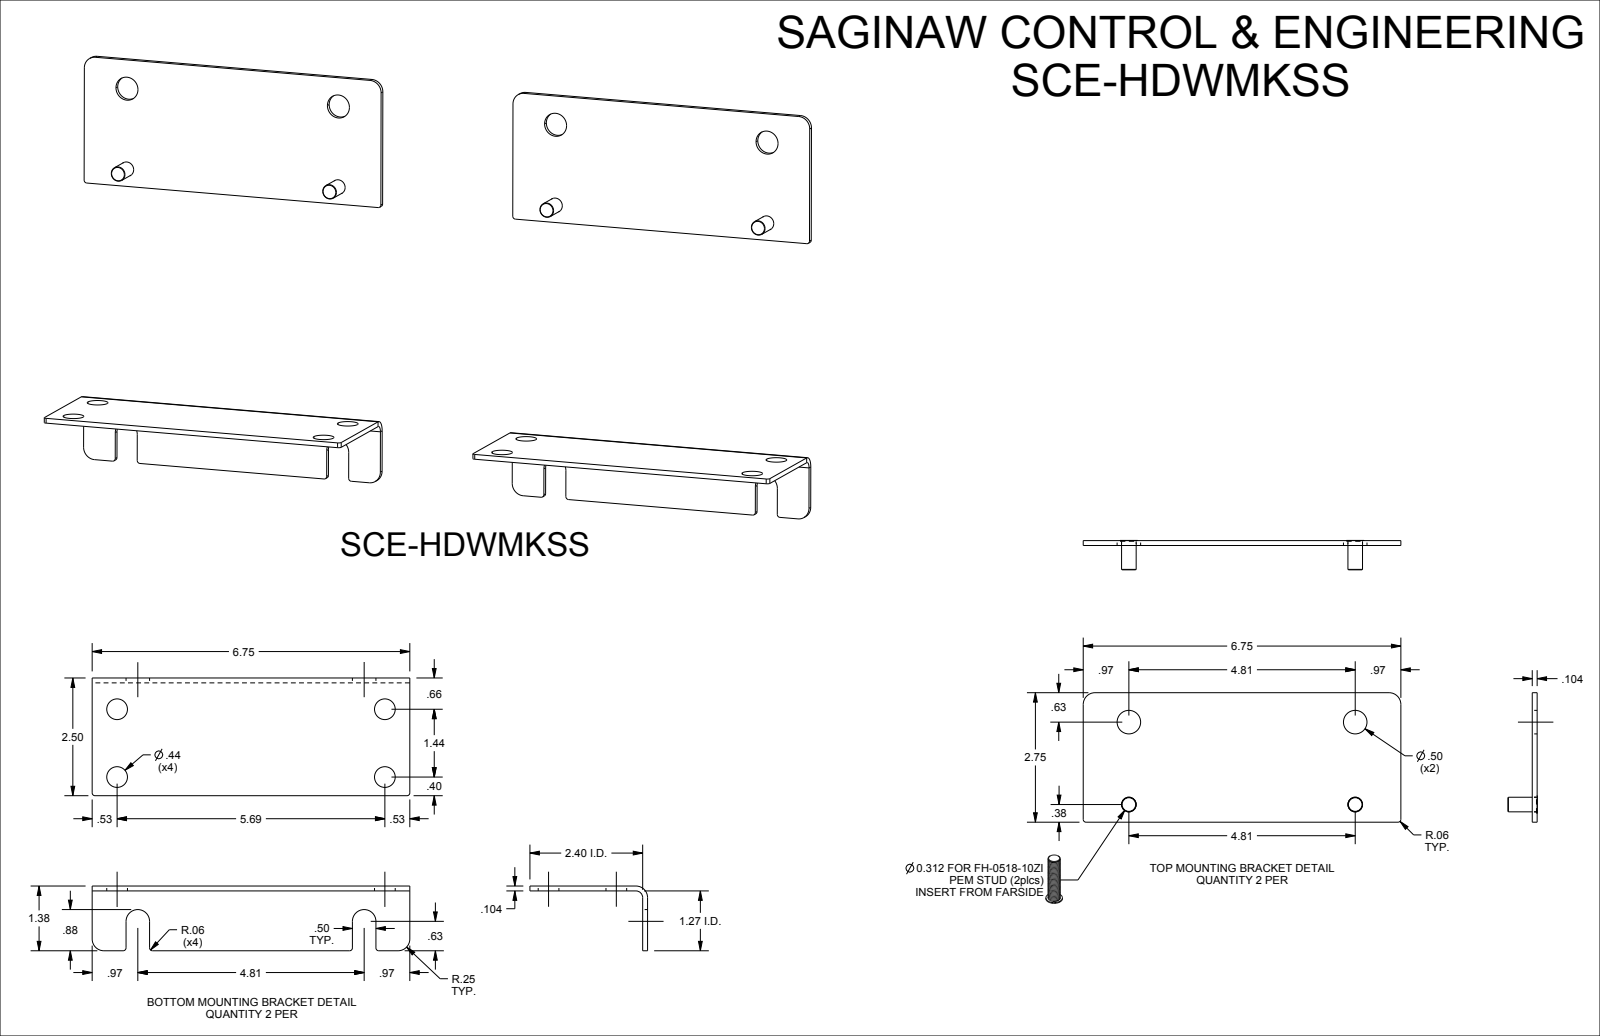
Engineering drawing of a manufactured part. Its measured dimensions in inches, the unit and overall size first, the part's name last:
Units: inches
Overall size (bounding box): 16.5 × 8.75 × 2.5
Round holes (diameter × count): ⌀0.44 ×8, ⌀0.312 ×4, ⌀0.5 ×4
Round bosses / shafts (diameter × count): ⌀0.376 ×4, ⌀0.31 ×4
Partial cylindrical surfaces — rounded edges, fillets, slot ends (radius × count): R0.25 ×21, R0.06 ×4, R0.062 ×3, R0.063 ×1, R0.125 ×1
Main face-to-face distances: 0.125, 4.75, 4.625, 7.5, 7.375, 2.75, 2.5, 2.375, 1.25, 1.375
Hole centre spacings: 9.75, 1.44, 1.75, 4.81, 5.119, 5.69, 5.869, 9.856
Volume: 10.5 in³ · Surface area: 181.4 in²
Bodies: 8 solids, 112 faces (52 planar, 56 cylindrical, 4 other)
Part name (STEP PRODUCT): SCE-HDWMK
STEP written by: SolidWorks 2019 (AUTOMOTIVE_DESIGN)
